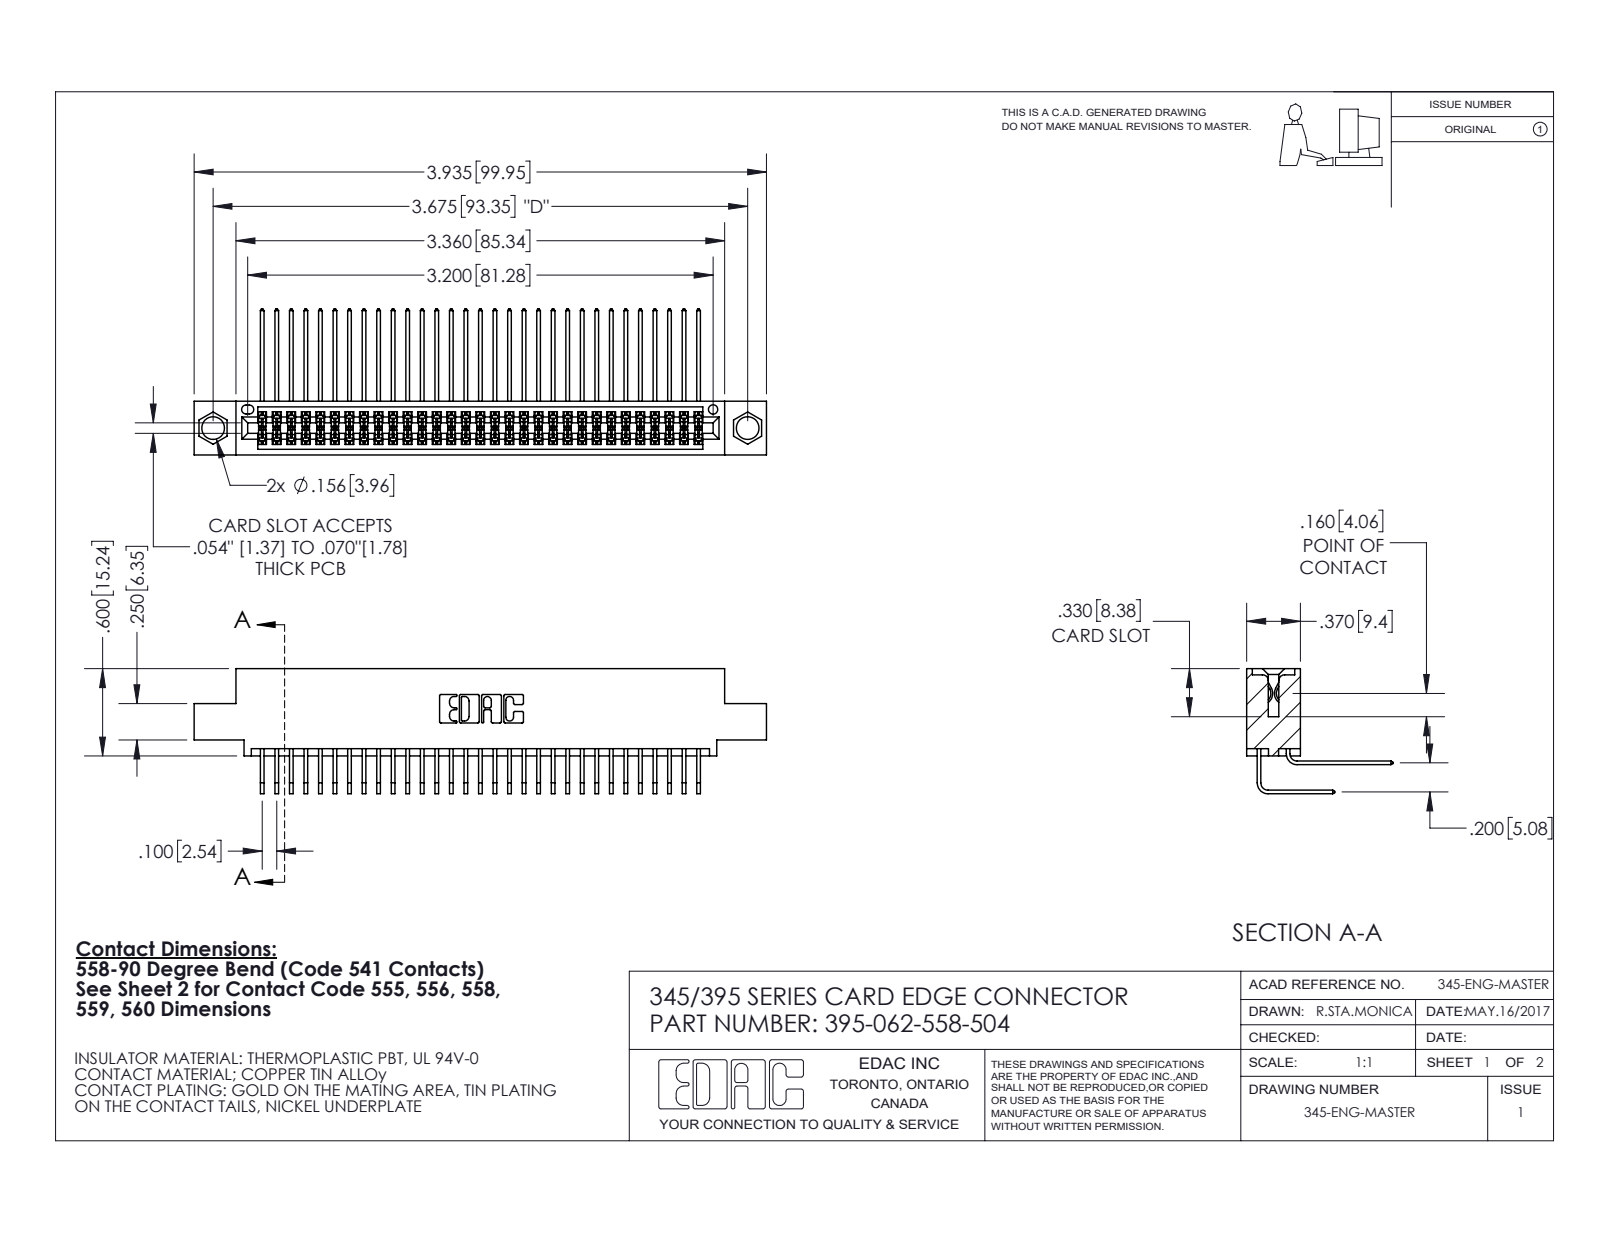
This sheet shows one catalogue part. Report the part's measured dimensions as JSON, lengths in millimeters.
{"part_name": "345 Part_0.110 Offset - 0.156 Dia-TI; 345-292-001_558 Tail - 2; 395-062-558-504; 345-292-001_558 559 Tail - 1", "step_written_by": "SolidWorks 2020 (CONFIG_CONTROL_DESIGN)", "units": "millimeters", "bodies": {"solids": 63, "faces": 3368, "planar": 2268, "cylindrical": 1100, "other": 0}, "overall_size": [99.9, 25.5, 21.8], "volume_mm3": 9780, "surface_area_mm2": 15880, "round_holes": [[4, 2], [1.6, 1]], "partial_cylinders_radius": [[0.2, 93], [0.3, 22], [0.2, 6], [0.8, 6], [0.7, 3], [0.4, 2], [0.5, 2], [0.6, 2]], "face_to_face_distances": [1.8, 7.6, 5.1, 9.4, 2.5, 6.9, 0.6, 5.7, 0.6, 4.4], "hole_center_spacings": [6.9, 87.4, 93.3]}
